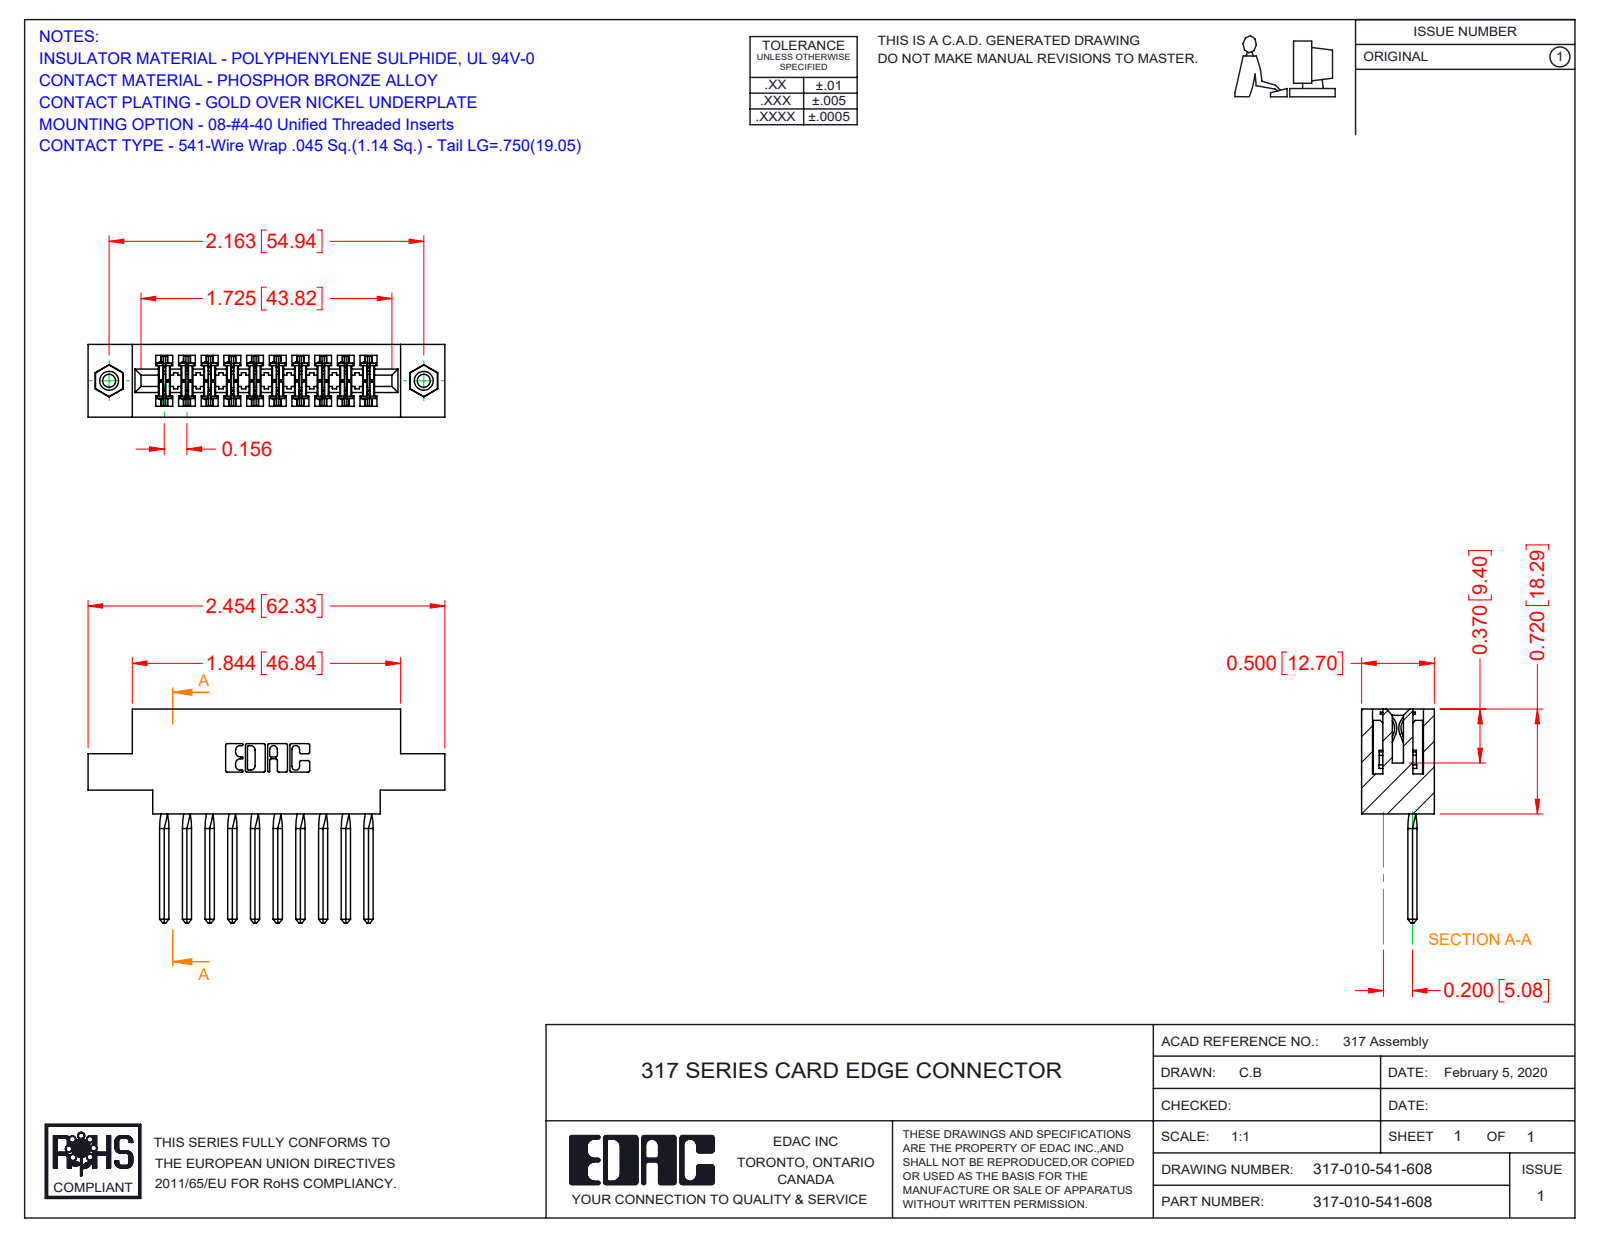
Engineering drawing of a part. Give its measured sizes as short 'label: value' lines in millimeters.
name: 317-290-002_541; 345-250-001_345-250-003-102; 317 Part_.156 Dia - TI; 317-010-541-678
written by: SolidWorks 2016 (CONFIG_CONTROL_DESIGN)
unit: mm
bodies: 13 solids, 1682 faces (1330 planar, 296 cylindrical, 56 other)
size: 62.3 × 37.3 × 12.7
volume: 9 110 mm³; area: 11 840 mm²
holes: 2× ⌀2.3, 2× ⌀3.2, 2× ⌀4
bosses: 2× ⌀3.9
rounds: 22× R0.3, 20× R0.4, 6× R0.2, 6× R0.8, 3× R0.7, 2× R2.4, 2× R2.5, 2× R2.8
face distances: 12.7, 1.9, 10.8, 2.8, 1.7, 5.6, 8.4, 8.9, 3.5, 4
hole spacings: 54.9
